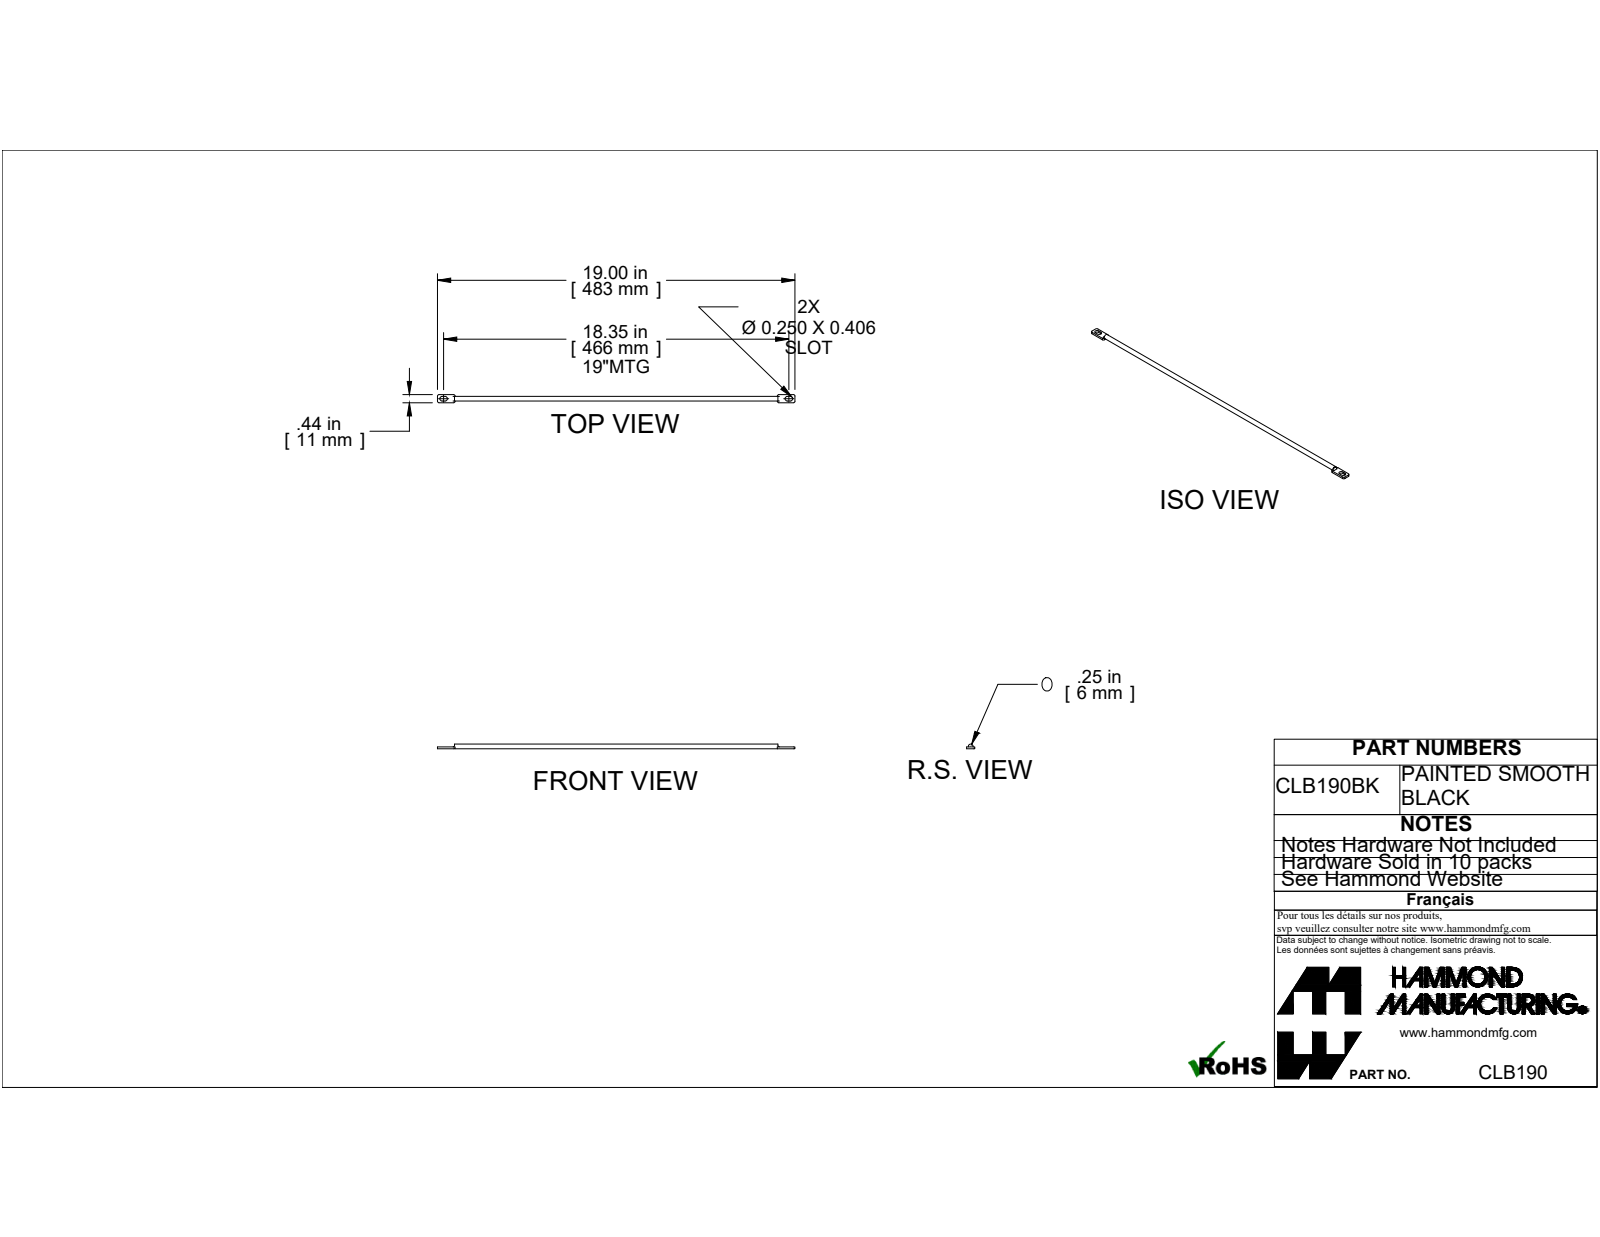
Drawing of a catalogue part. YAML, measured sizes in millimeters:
step_written_by: "Unknown (AUTOMOTIVE_DESIGN)"
units: millimeters
bodies: {solids: 1, faces: 35, planar: 20, cylindrical: 15, other: 0}
overall_size: [482.6, 11.05, 6.35]
volume: 14771
surface_area: 9947
round_bosses_or_shafts:
  - {diameter: 6.35, count: 1}
partial_cylinders:
  - {radius: 2.03, count: 10}
  - {radius: 3.17, count: 4}
face_to_face_distances: [2.53, 11.04, 2.35, 8.69, 6.34, 482.6, 23.01, 459.59, 23.81, 458.79]
